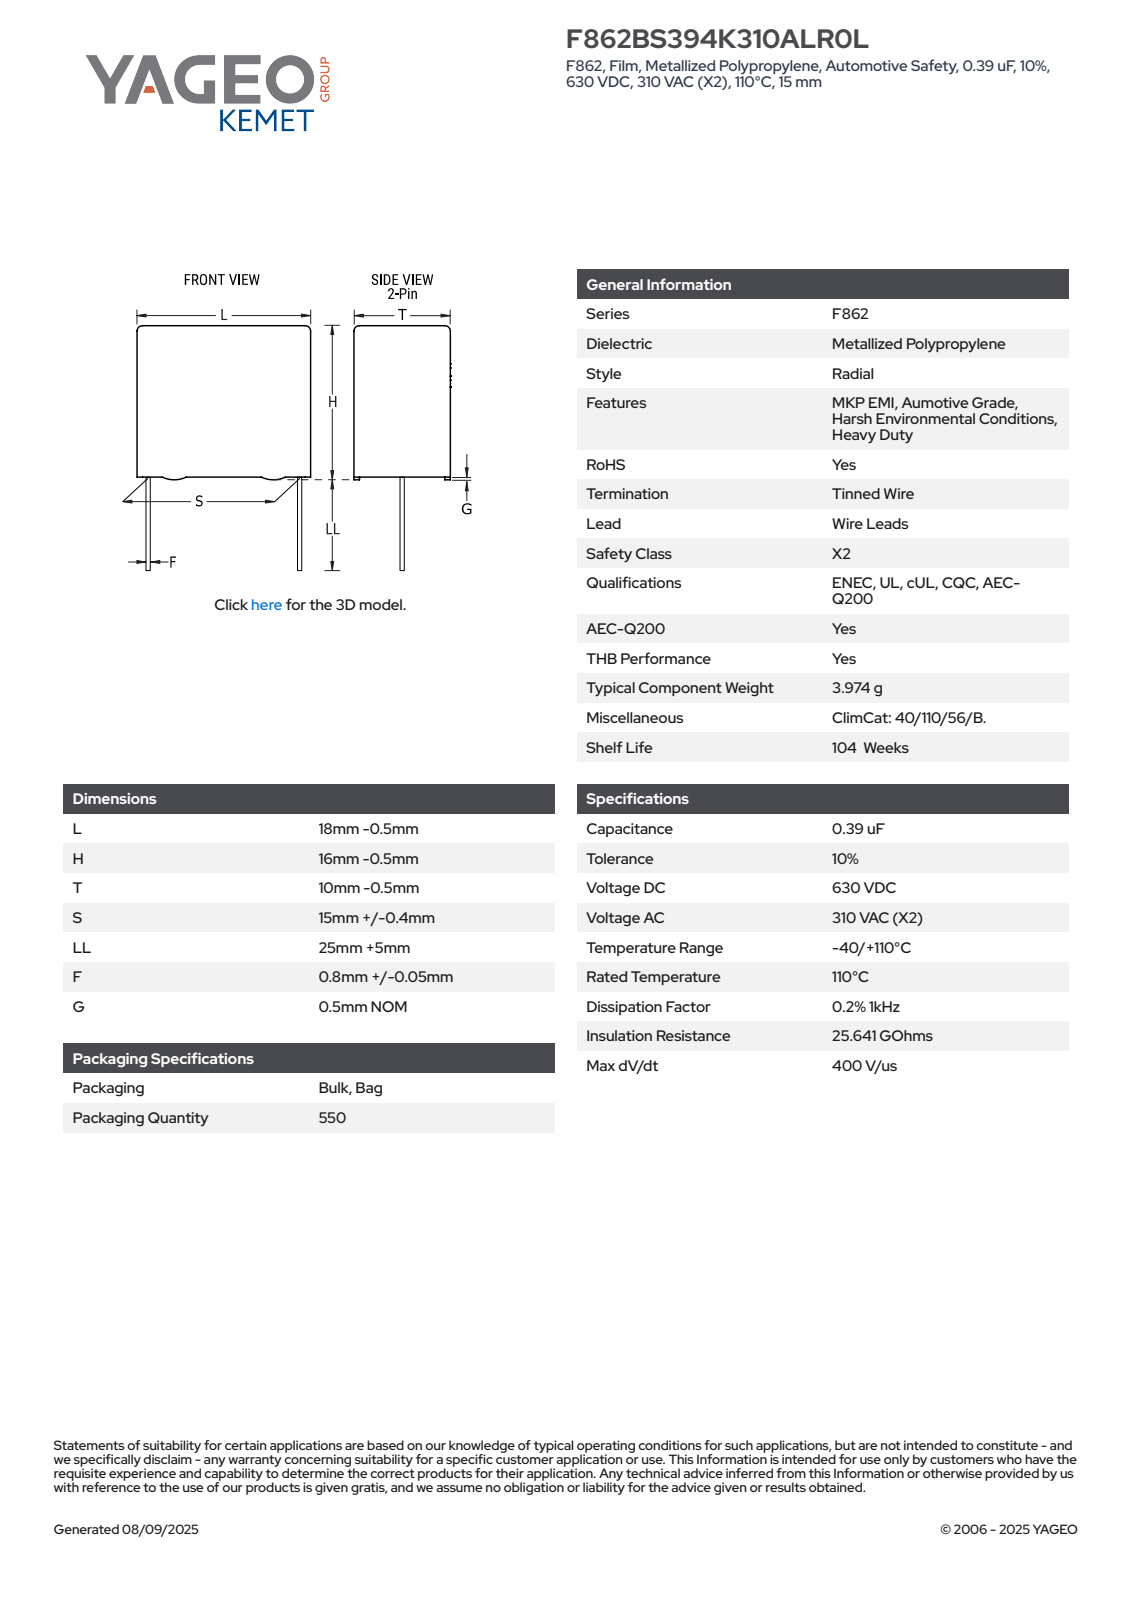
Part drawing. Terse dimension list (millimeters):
name: CFR_RBG_18X16X10_L17.5H15.5T9.5S15LL30F0.85G0.5
written by: SolidWorks 2014 (AUTOMOTIVE_DESIGN)
unit: mm
bodies: 4 solids, 89 faces (81 planar, 8 cylindrical, 0 other)
size: 45.5 × 17.5 × 9.51
volume: 2 529 mm³; area: 1 340 mm²
bosses: 2× ⌀0.85
rounds: 4× R0.5
face distances: 9.5, 15, 17.5, 0.5, 15.5, 0.54, 8.96, 8.42, 30, 30.5
